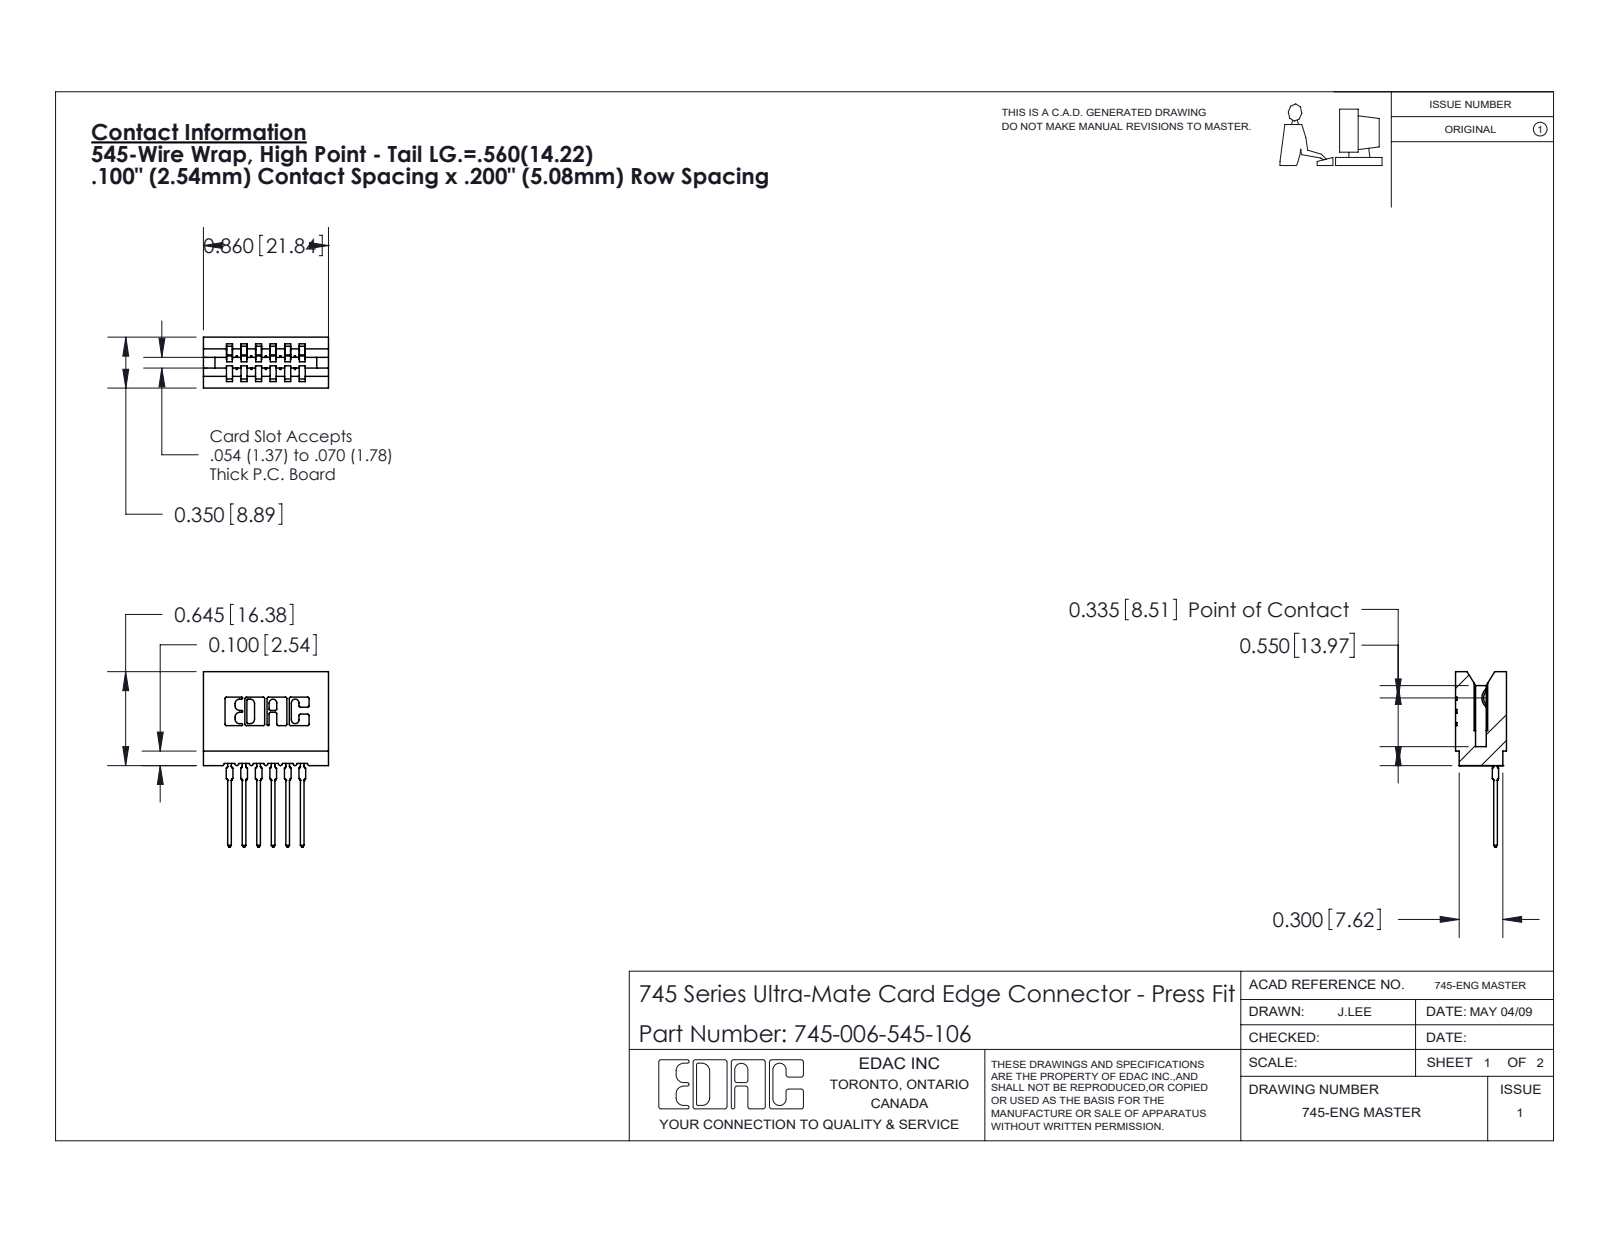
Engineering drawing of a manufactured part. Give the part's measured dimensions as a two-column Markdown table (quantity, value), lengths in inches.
| quantity | value |
| --- | --- |
| part name | 745 Part_Insulator Option - 06; 745-292-001_545; 745-006-545-106 |
| STEP written by | SolidWorks 2020 (CONFIG_CONTROL_DESIGN) |
| units | inches |
| bodies | 7 solids, 768 faces (458 planar, 154 cylindrical, 156 other) |
| overall size | 1.206 × 0.86 × 0.35 |
| volume | 0.13 in³ |
| surface area | 5.209 in² |
| partial cylindrical surfaces (radius × count) | 0.01 × 22, 0.015 × 12, 0.021 × 12, 0.007 × 6, 0.031 × 6, 0.005 × 4, 0.011 × 4, 0.026 × 3 |
| main face-to-face distances | 0.1, 0.2, 0.3, 0.042, 0.142, 0.058, 0.242, 0.158, 0.4, 0.35 |
